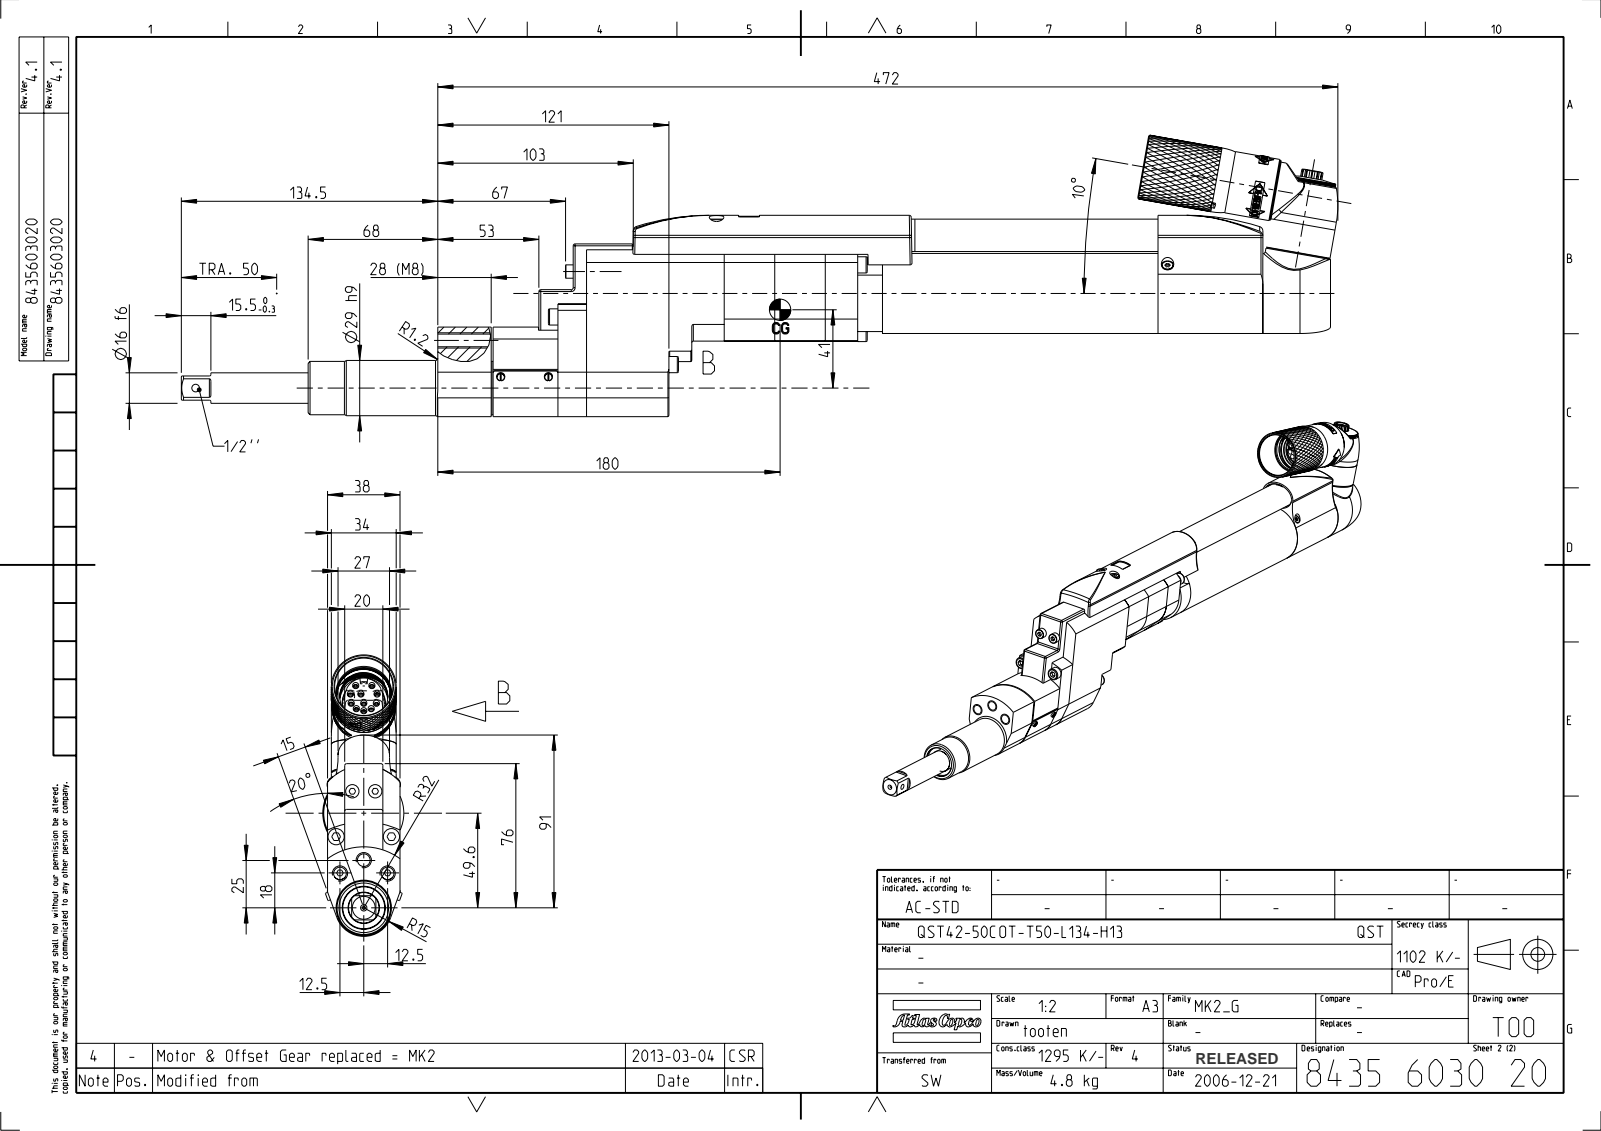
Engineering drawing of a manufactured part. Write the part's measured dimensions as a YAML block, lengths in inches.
part_name: "4230260102; 4230260112_ASM; 4230262500; 4230262900 (+8 more)"
step_written_by: "CREO PARAMETRIC BY PTC INC, 2022414 (CONFIG_CONTROL_DESIGN)"
units: inches
bodies: {solids: 35, faces: 3240, planar: 1211, cylindrical: 1122, other: 907}
overall_size: [23.878, 5.815, 1.654]
volume: 31.33
surface_area: 444.4
round_holes:
  - {diameter: 0.128, count: 10}
  - {diameter: 0.13, count: 7}
  - {diameter: 0.118, count: 6}
  - {diameter: 0.177, count: 6}
  - {diameter: 0.138, count: 5}
  - {diameter: 0.154, count: 5}
  - {diameter: 0.217, count: 5}
  - {diameter: 0.079, count: 4}
  - {diameter: 0.055, count: 3}
  - {diameter: 0.116, count: 3}
  - {diameter: 0.169, count: 3}
  - {diameter: 0.262, count: 3}
round_bosses_or_shafts:
  - {diameter: 0.197, count: 8}
  - {diameter: 0.335, count: 7}
  - {diameter: 0.157, count: 5}
  - {diameter: 1.339, count: 4}
  - {diameter: 0.165, count: 4}
  - {diameter: 0.087, count: 4}
  - {diameter: 0.098, count: 3}
  - {diameter: 1.181, count: 2}
partial_cylinders:
  - {radius: 0.039, count: 22}
  - {radius: 0.079, count: 9}
  - {radius: 0.031, count: 6}
  - {radius: 0.008, count: 4}
  - {radius: 0.207, count: 4}
  - {radius: 1.575, count: 4}
  - {radius: 0.256, count: 3}
  - {radius: 0.016, count: 2}
face_to_face_distances: [1.496, 1.142, 0.039, 0.354, 0.02, 1.102, 0.591, 1.043, 0.748, 6.11]
hole_center_spacings: [0.984, 0.627, 0.749, 1.576, 0.472, 0.591, 0.199, 0.517]
